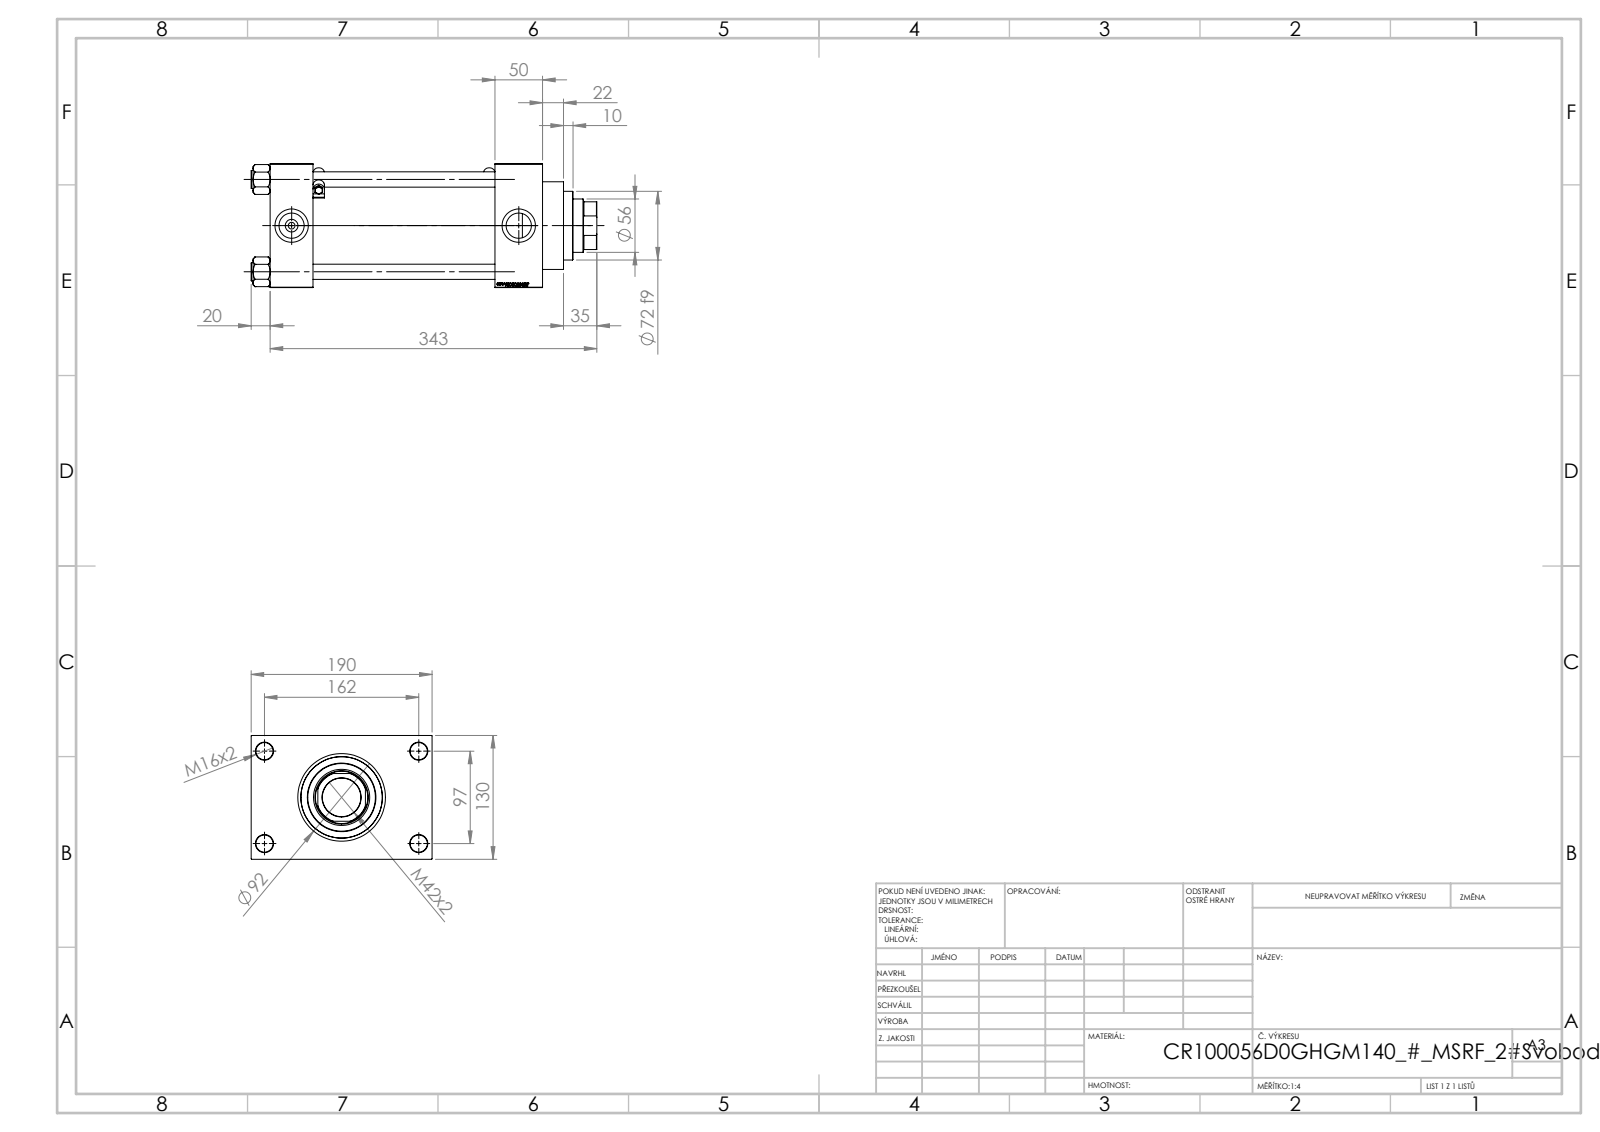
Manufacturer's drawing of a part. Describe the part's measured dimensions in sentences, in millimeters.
The part is named "V215CR_VCP_D; NUT_M5_D; V215_VC_A; V215CR_D_TYCINKA (+2 more)". Its 3-D file was written by "SolidWorks 2019 (CONFIG_CONTROL_DESIGN)". It is 13 solids with 1215 faces: 581 planar, 116 cylindrical and 518 other. Overall it measures 363 by 190 by 130 millimeters. Its volume is 3 144 000 cubic millimeters and its surface area 489 971 square millimeters. Round holes: 4 of diameter 16, 4 of diameter 18, 2 of diameter 7, 2 of diameter 26.44, 2 of diameter 35, 1 of diameter 40.5, 1 of diameter 56, 1 of diameter 59, 1 of diameter 76, 1 of diameter 85.5, 1 of diameter 100. Round bosses or shafts: 4 of diameter 19, 2 of diameter 5, 2 of diameter 2.5, 1 of diameter 106, 1 of diameter 92, 1 of diameter 72. Partial cylindrical surfaces (rounded edges, fillets, slot ends): 12 of radius 0.5, 4 of radius 6, 1 of radius 27. The main face-to-face distances are 130, 50, 45, 236, 191, 286, 241, 30, 190, 160. The hole center spacings are 32.55, 68.52, 94.41, 96.9, 102.27, 129.45, 161.73, 97.
